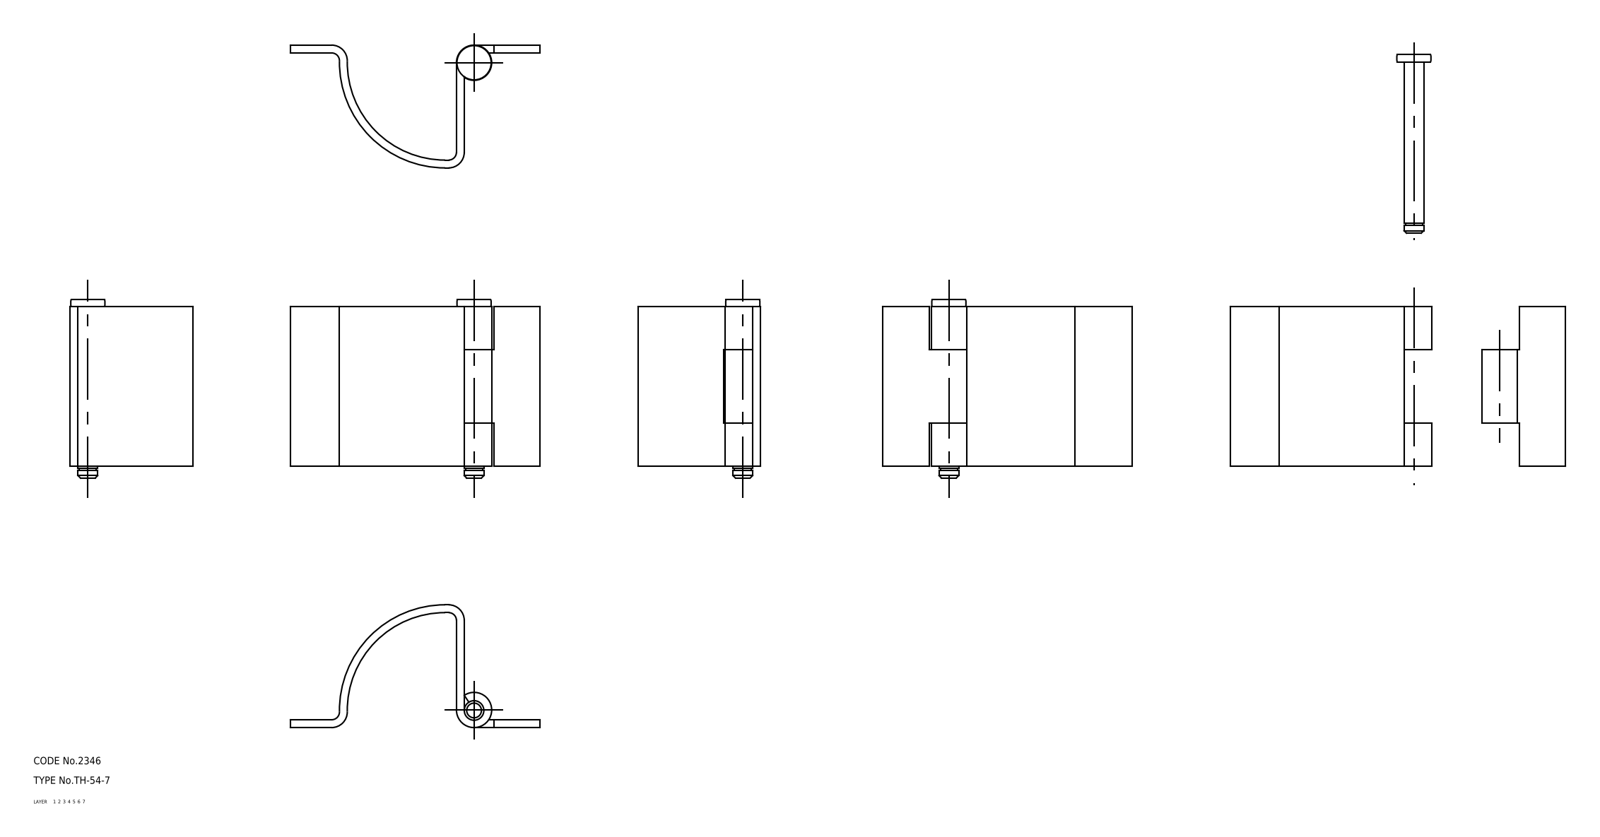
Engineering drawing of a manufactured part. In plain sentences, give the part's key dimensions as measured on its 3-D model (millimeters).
The part is named "shaft; hinge piece_B; hinge piece_A; TH_54_7_11315_36". Its 3-D file was written by "CADfix (AUTOMOTIVE_DESIGN)". It is 3 solids with 50 faces: 0 planar, 0 cylindrical and 50 other. Overall it measures 102 by 73 by 50 millimeters. Its volume is 42 322 cubic millimeters and its surface area 28 655 square millimeters.
